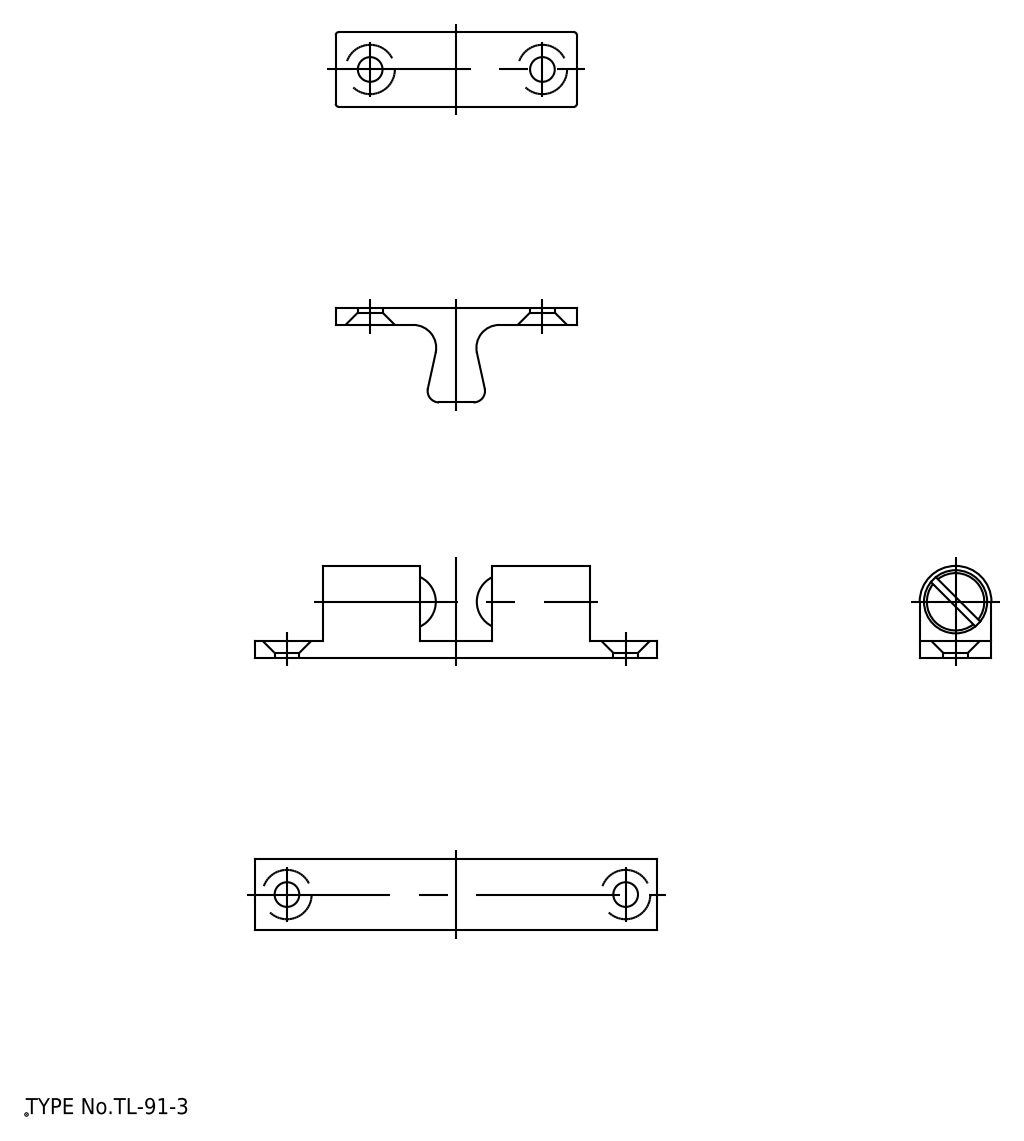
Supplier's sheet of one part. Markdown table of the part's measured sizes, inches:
| quantity | value |
| --- | --- |
| part name | screw; ball; keeper; housing |
| STEP written by | spGate 19.8.4 (****-****-****-****) (AUTOMOTIVE_DESIGN) |
| units | inches |
| bodies | 6 solids, 86 faces (36 planar, 26 cylindrical, 24 other) |
| overall size | 2.756 × 2.647 × 0.512 |
| volume | 0.574 in³ |
| surface area | 11.66 in² |
| round holes (diameter × count) | 0.169 × 4, 0.375 × 1, 0.433 × 1 |
| partial cylindrical surfaces (radius × count) | 0.079 × 2, 0.157 × 2, 0.246 × 1 |
| main face-to-face distances | 0.118, 2.529, 0.492, 2.647, 0.502, 0.512, 2.411, 0.669, 1.161, 0.157 |
| hole center spacings | 0.571, 1.752, 1.181, 2.323 |
